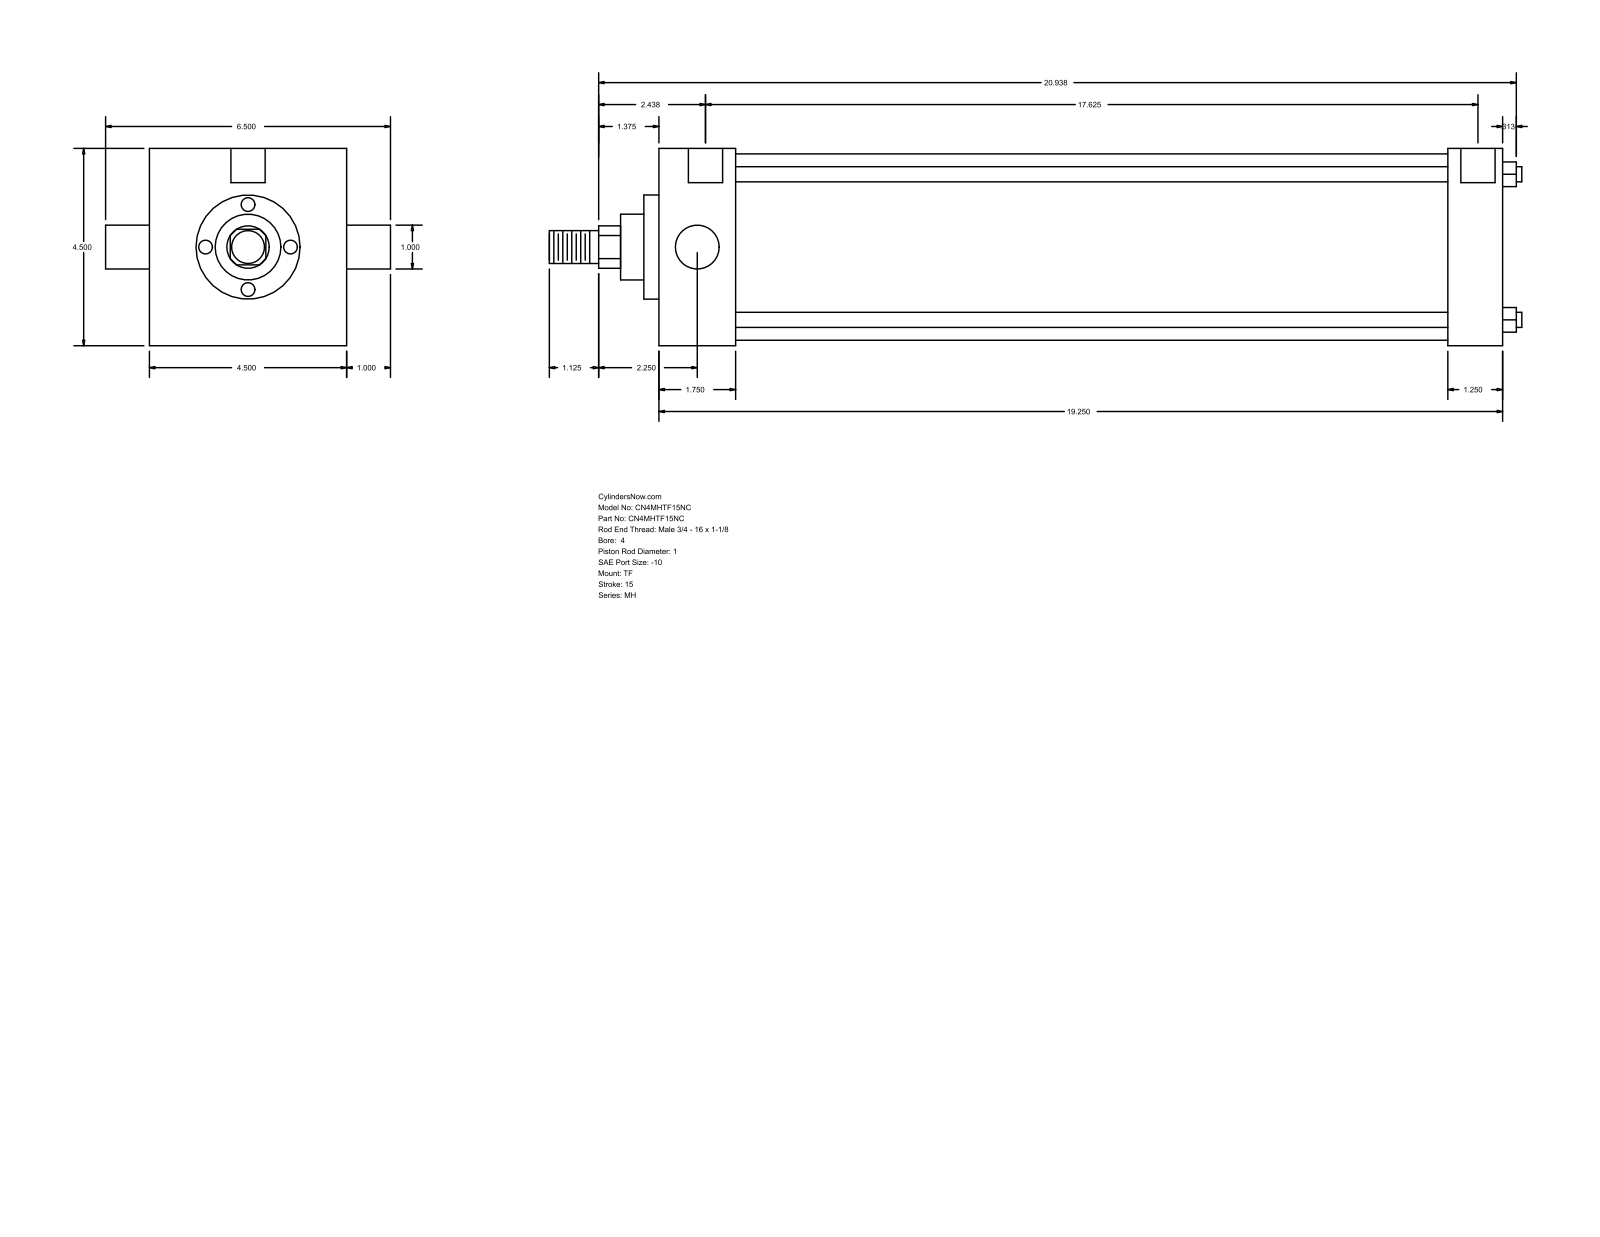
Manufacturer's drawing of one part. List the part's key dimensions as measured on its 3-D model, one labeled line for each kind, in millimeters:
Part name (STEP PRODUCT): MH_TF__0400_1
STEP written by: GSSL Pune (CONFIG_CONTROL_DESIGN)
Units: millimetres
Bodies: 0 solids, 86 faces (61 planar, 25 cylindrical, 0 other)
Overall size (bounding box): 563.56 × 165.1 × 114.3
Round holes (diameter × count): ⌀8.73 ×3, ⌀19.84 ×2
Round bosses / shafts (diameter × count): ⌀8.76 ×4, ⌀25.4 ×2, ⌀107.95 ×1, ⌀60.33 ×1, ⌀38.1 ×1, ⌀19.05 ×1
Partial cylindrical surfaces — rounded edges, fillets, slot ends (radius × count): R12.29 ×1
Main face-to-face distances: 114.3, 488.96, 44.46, 444.5, 457.2, 412.74, 31.76, 8.73, 53.19, 465.93
Hole centre spacings: 1.58, 1.59, 447.68, 449.26, 449.27, 450.85
